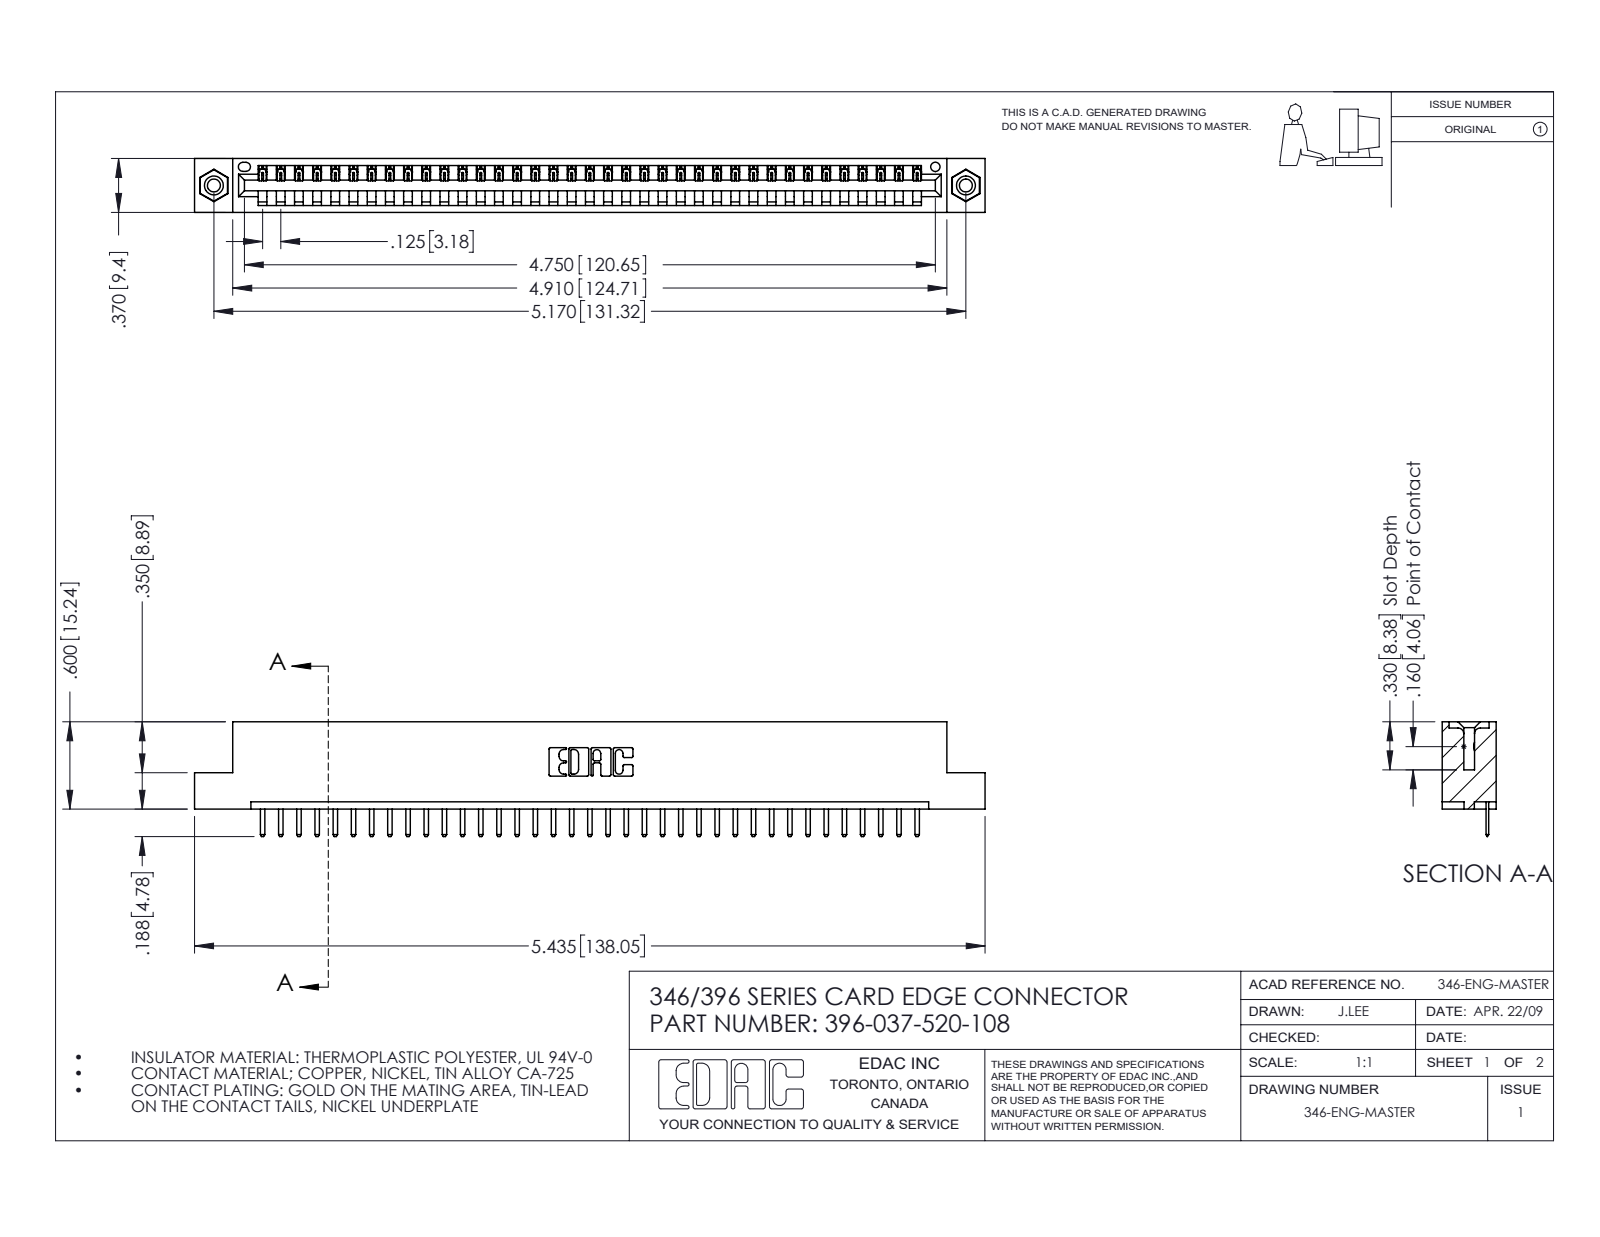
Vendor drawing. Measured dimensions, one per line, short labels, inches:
name: 396-037-520-108; 345-292-001_345-293-120; 346 Part_Flush Mounting Lugs - 0.156 Dia-TI; 345-250-001_345-250-003-102
written by: SolidWorks 2016 (CONFIG_CONTROL_DESIGN)
unit: in
bodies: 40 solids, 2476 faces (1662 planar, 798 cylindrical, 16 other)
size: 5.435 × 0.788 × 0.37
volume: 0.797 in³; area: 24.71 in²
holes: 2× ⌀0.089, 2× ⌀0.125, 2× ⌀0.156, 1× ⌀0.064
bosses: 2× ⌀0.155
rounds: 76× R0.01, 74× R0.006, 22× R0.01, 6× R0.007, 6× R0.031, 3× R0.026, 2× R0.031, 2× R0.04
face distances: 0.048, 0.322, 0.37, 0.25, 0.148, 0.222, 0.1, 0.174, 0.072, 0.298
hole spacings: 0.246, 4.961, 5.17
